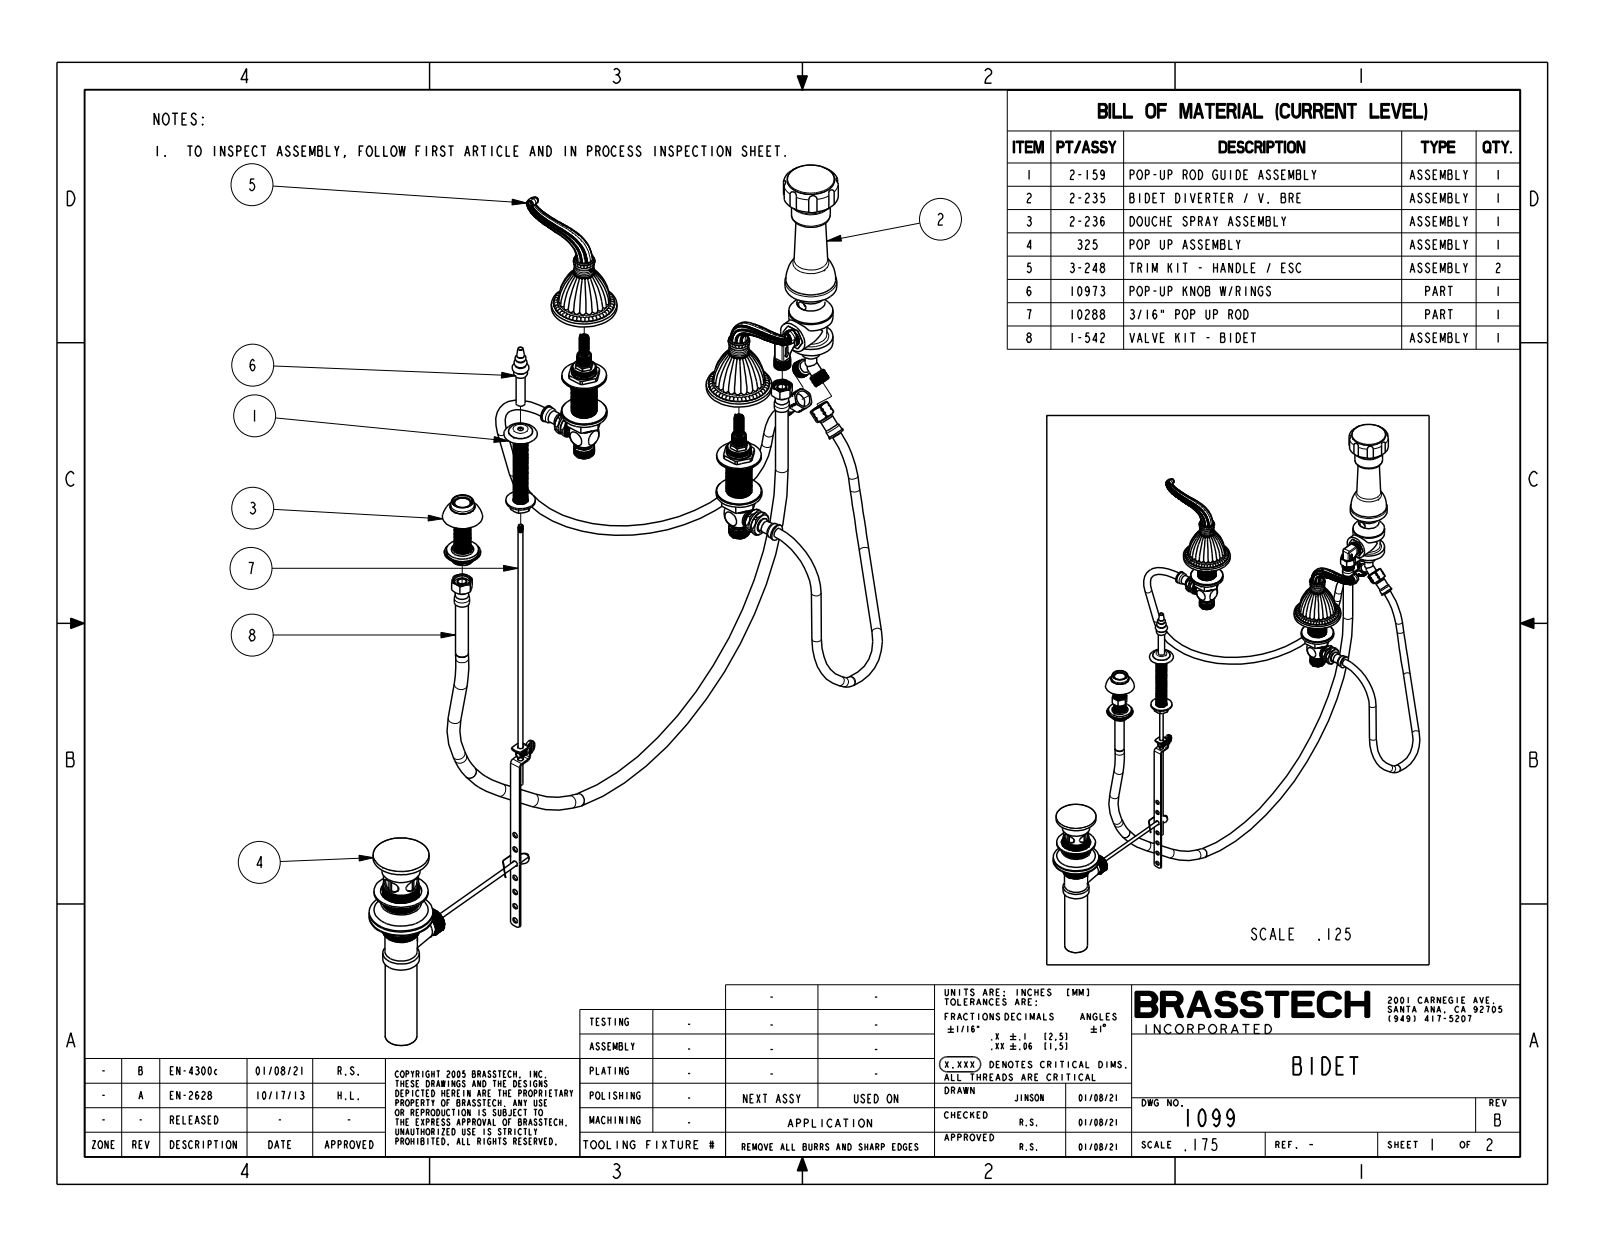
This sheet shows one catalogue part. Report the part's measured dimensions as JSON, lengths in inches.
{"part_name": "1099", "step_written_by": "CREO PARAMETRIC BY PTC INC, 2018400 (CONFIG_CONTROL_DESIGN)", "units": "inches", "bodies": {"solids": 5, "faces": 6362, "planar": 700, "cylindrical": 2248, "other": 3414}, "overall_size": [22.855, 13.766, 5.353], "volume_in3": 23.1, "surface_area_in2": 112.4, "round_holes": [[0.04, 378], [0.05, 98], [0.045, 46], [0.041, 22], [0.625, 1], [0.792, 1], [0.94, 1]], "round_bosses_or_shafts": [[0.775, 3], [2.57, 2], [0.79, 2], [0.4, 2], [2.025, 1], [1.52, 1], [0.925, 1], [0.44, 1]], "partial_cylinders_radius": [[0.21, 8], [0.357, 1], [1.077, 1]], "face_to_face_distances": [1.84, 3.468, 1.628, 1.81, 0.03, 1.658, 0.674, 1.136, 1.166, 2.794], "hole_center_spacings": [0.05, 0.239, 0.05, 0.061, 0.144, 0.151, 0.157, 0.189]}
